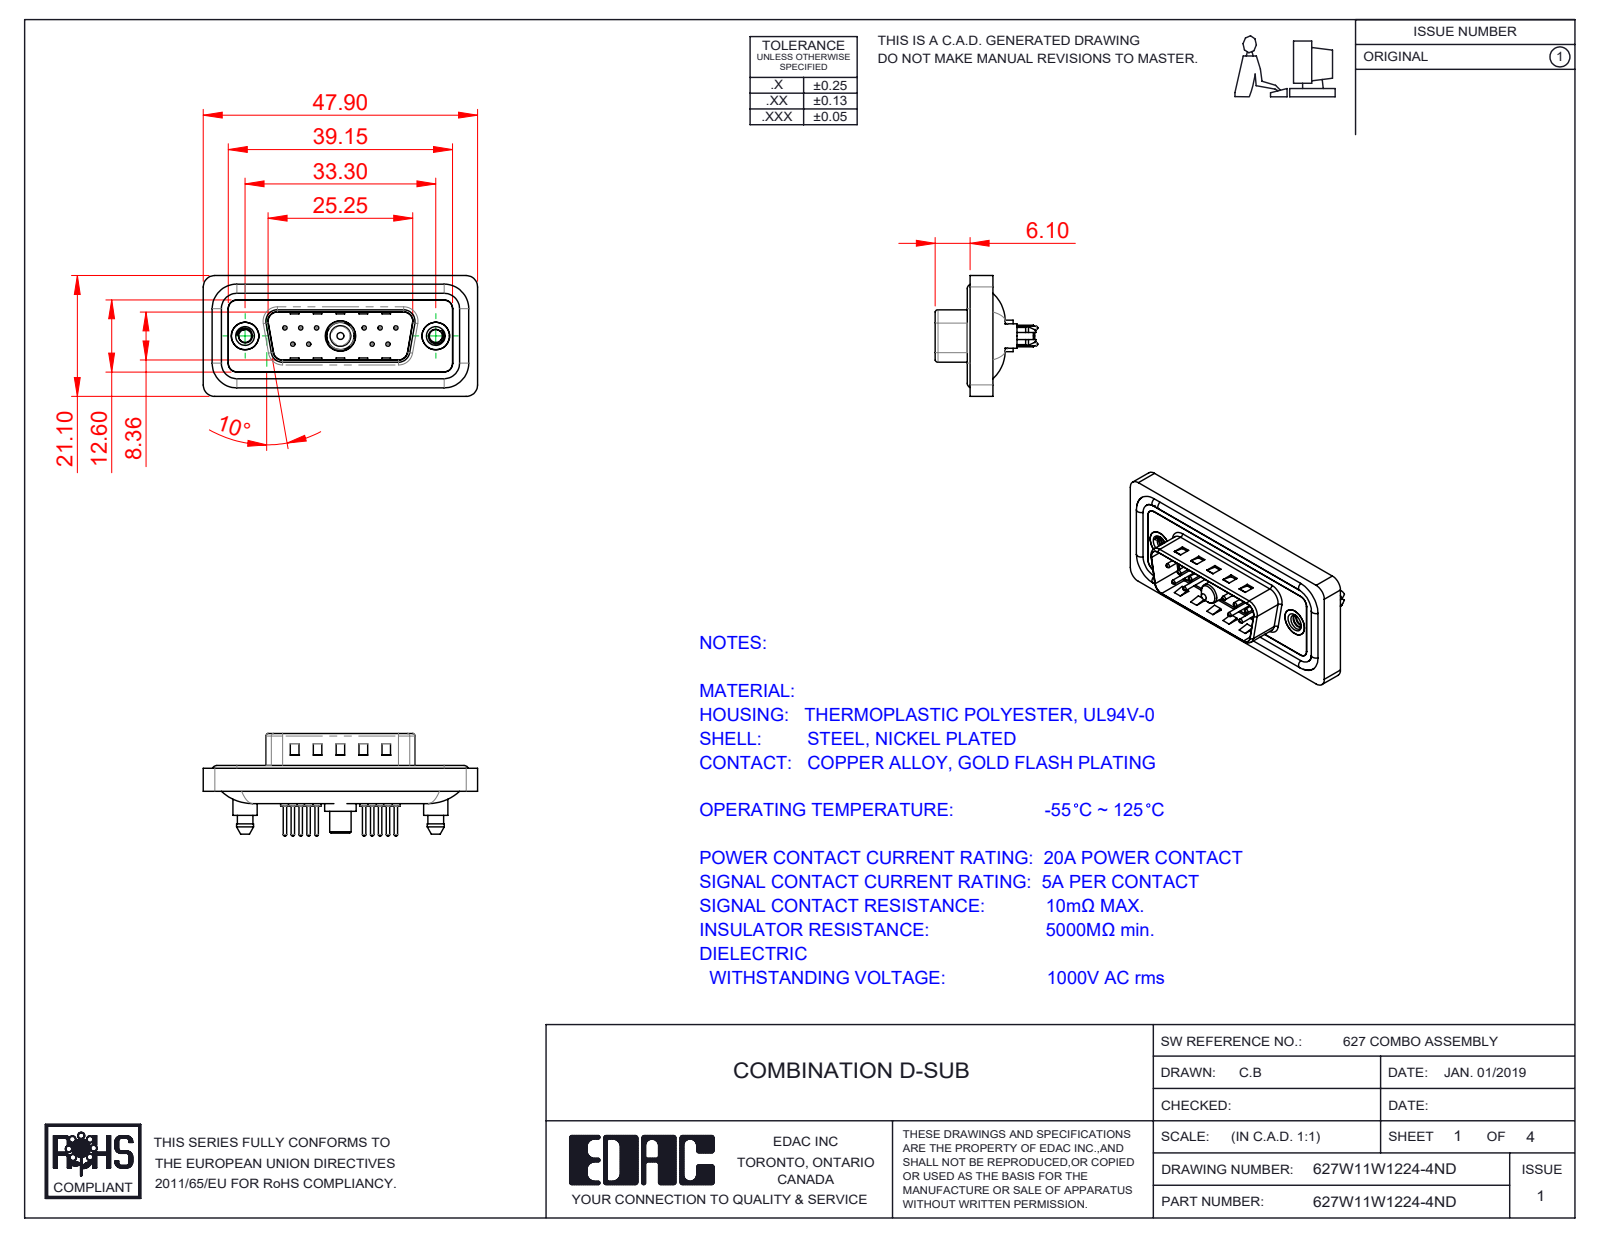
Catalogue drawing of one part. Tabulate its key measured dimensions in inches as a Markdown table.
| quantity | value |
| --- | --- |
| part name | 627Combo Contact Row 1_24; 627W11W1224-4ND; 627Combo Waterproof Housing_15 Contacts; 627Combo Contact Row 2_24 (+6 more) |
| STEP written by | SolidWorks 2020 (CONFIG_CONTROL_DESIGN) |
| units | inches |
| bodies | 19 solids, 927 faces (282 planar, 387 cylindrical, 258 other) |
| overall size | 1.886 × 0.831 × 0.705 |
| volume | 0.342 in³ |
| surface area | 14.23 in² |
| round holes (diameter × count) | 0.03 × 10, 0.063 × 10, 0.079 × 10, 0.089 × 2, 0.157 × 2, 0.189 × 2, 0.197 × 2, 0.191 × 1, 0.209 × 1 |
| round bosses / shafts (diameter × count) | 0.059 × 10, 0.024 × 10, 0.063 × 4, 0.213 × 2, 0.193 × 2, 0.167 × 2, 0.217 × 1, 0.205 × 1 |
| partial cylindrical surfaces (radius × count) | 0.059 × 28, 0.079 × 20, 0.063 × 10, 0.02 × 8, 0.039 × 7, 0.01 × 4, 0.024 × 4, 0.026 × 4 |
| main face-to-face distances | 0.016, 0.043, 0.063, 0.059, 0.122, 0.114, 0.02, 0.161, 0.032, 0.377 |
| hole center spacings | 0.124, 0.109, 0.545, 0.436, 0.654, 0.198, 0.198, 0.218 |
